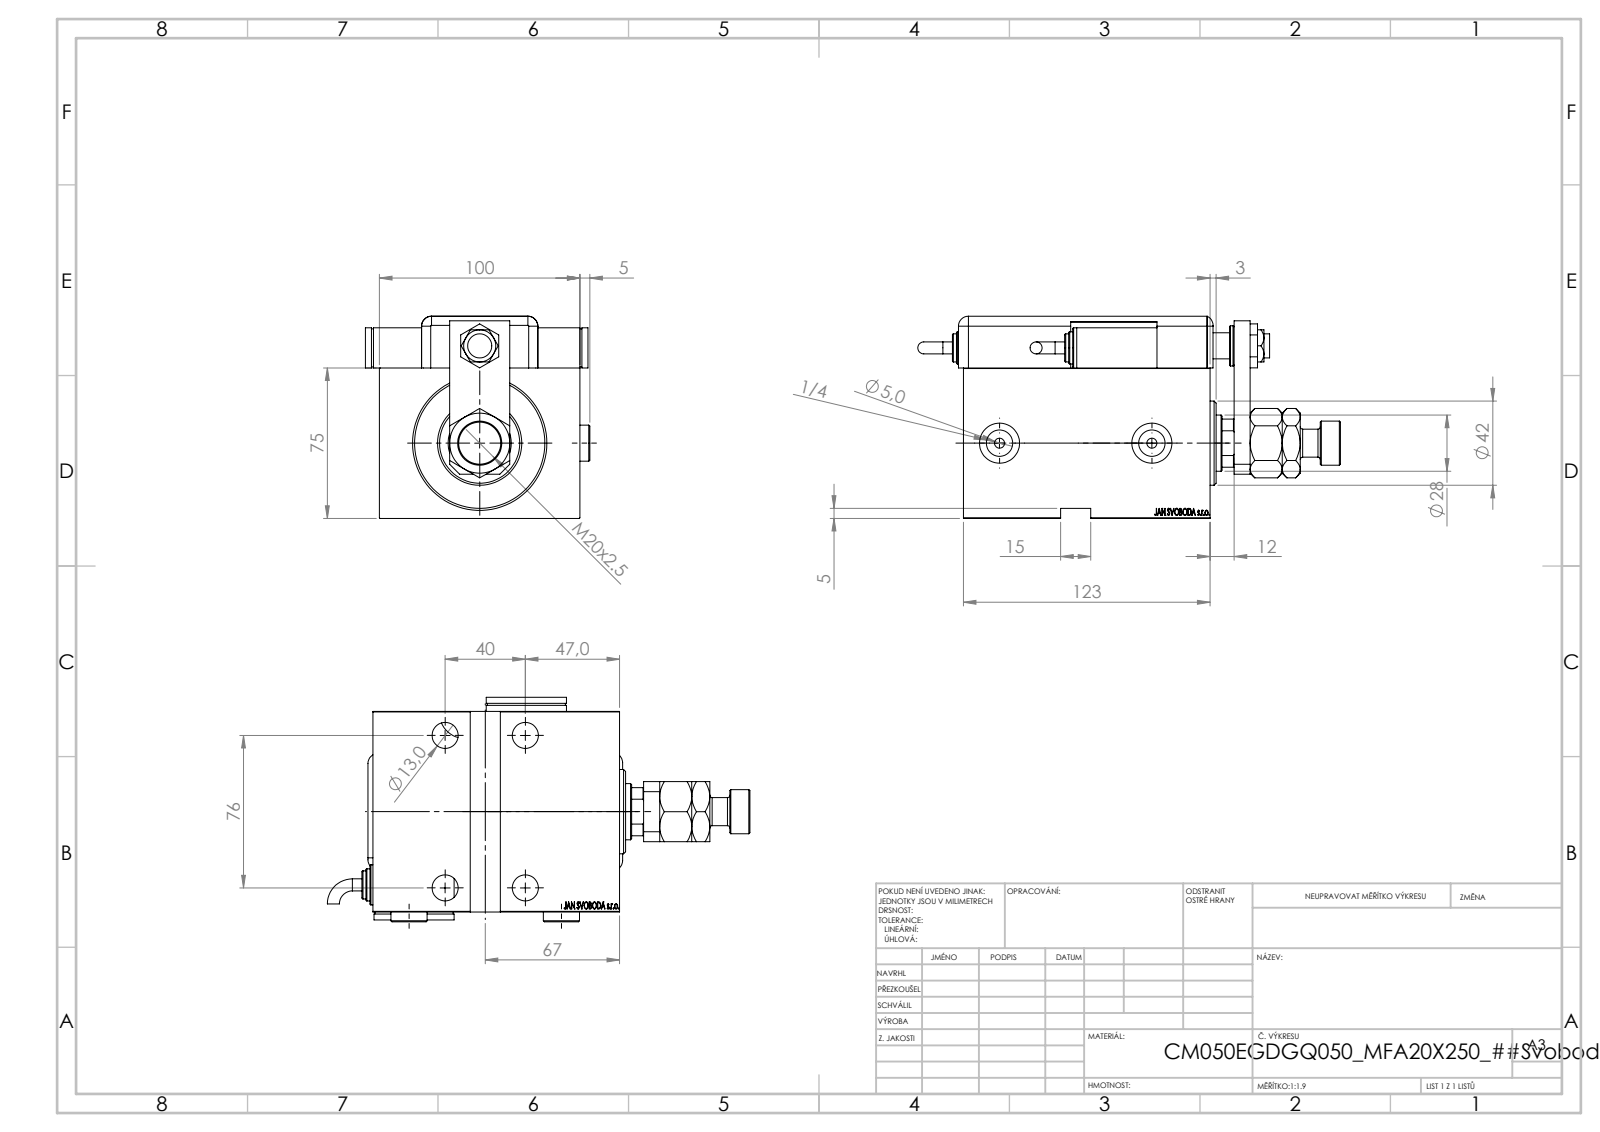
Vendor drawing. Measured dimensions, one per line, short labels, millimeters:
name: NUT_D13; SWITCH_Q_FRONT_BACK; MAGNETIC SWITCH Q; V450CM_E_VCP (+8 more)
written by: SolidWorks 2019 (CONFIG_CONTROL_DESIGN)
unit: mm
bodies: 16 solids, 1348 faces (668 planar, 127 cylindrical, 553 other)
size: 210.76 × 111.9 × 100.8
volume: 976 257 mm³; area: 189 107 mm²
holes: 5× ⌀13, 4× ⌀19, 3× ⌀20, 2× ⌀4, 2× ⌀5, 2× ⌀8, 2× ⌀13.16, 1× ⌀12, 1× ⌀14, 1× ⌀18.5, 1× ⌀28, 1× ⌀31.5
bosses: 3× ⌀20, 3× ⌀14, 2× ⌀18, 2× ⌀16, 2× ⌀6, 1× ⌀52, 1× ⌀42, 1× ⌀22
rounds: 9× R5, 1× R10, 1× R13.5
face distances: 3, 75, 100, 14, 20, 123, 100.8, 25.8, 109, 25
hole spacings: 76, 40, 47.2, 61.22, 82.87, 85.88, 91.59, 20
